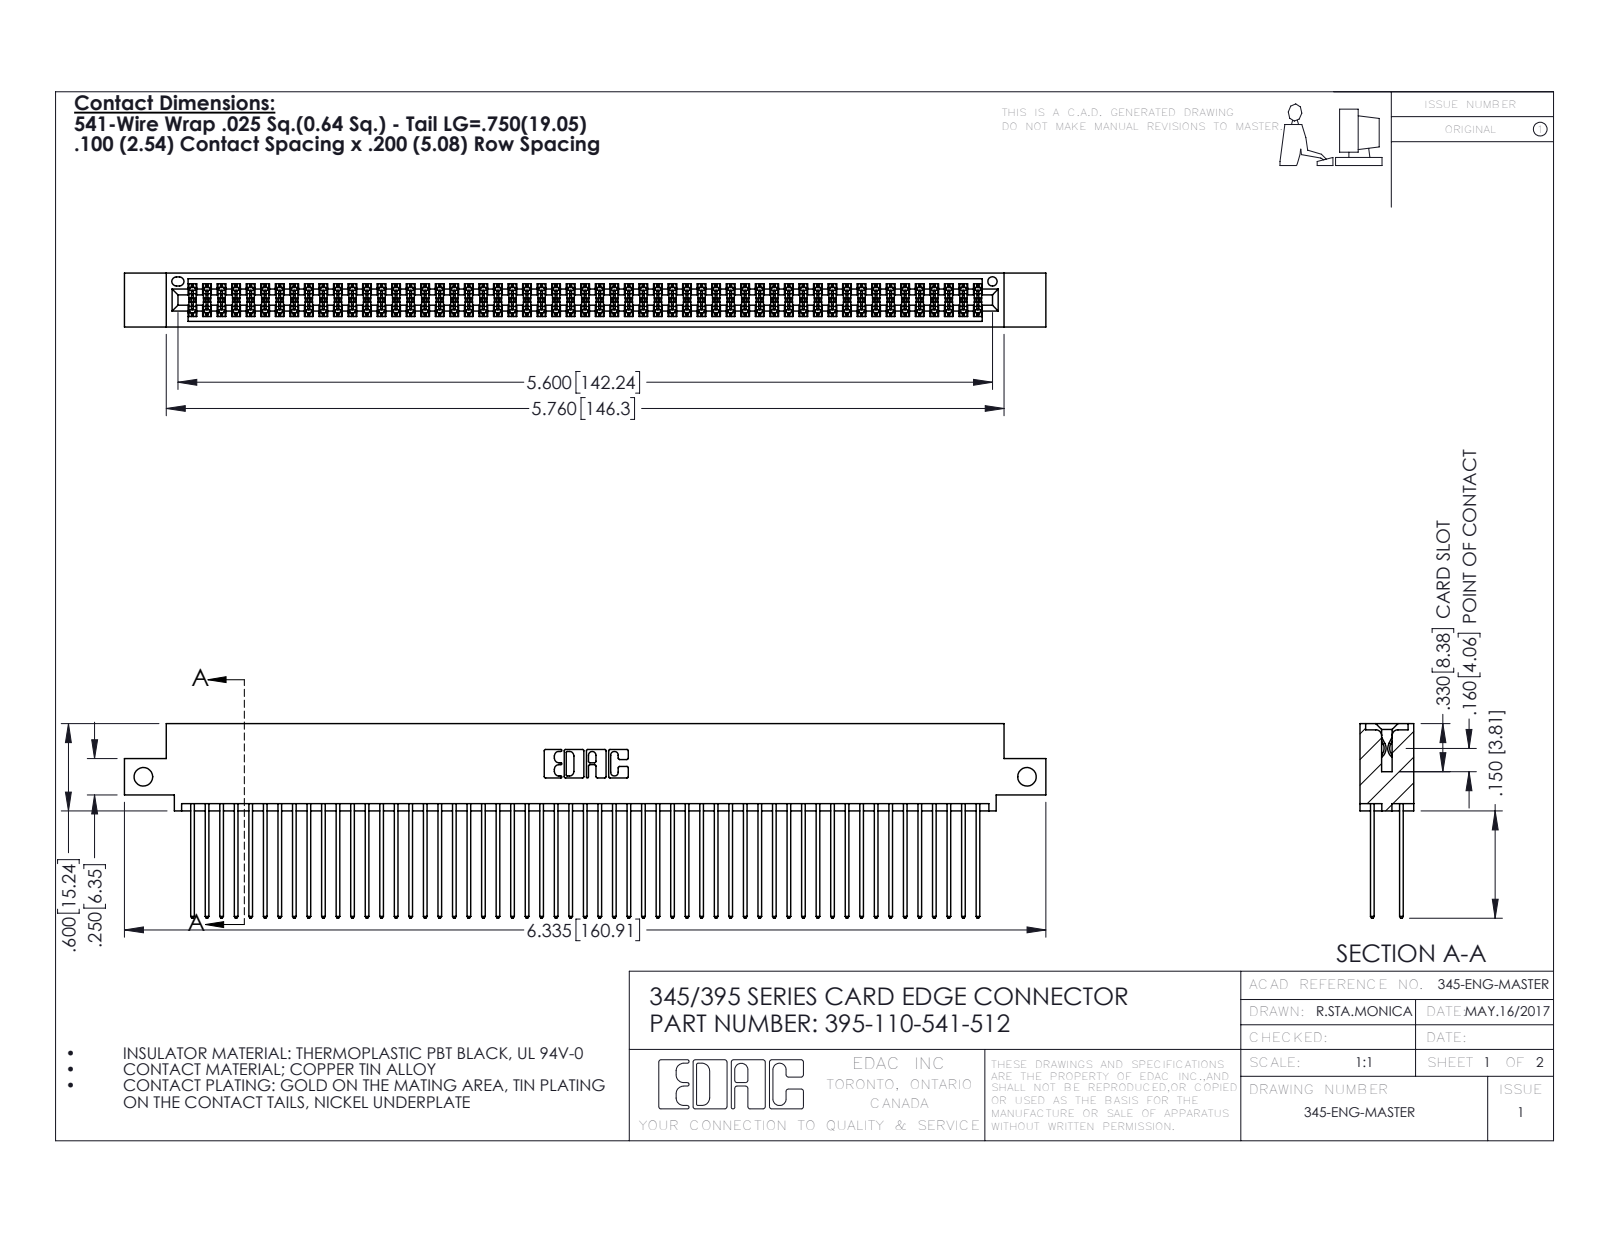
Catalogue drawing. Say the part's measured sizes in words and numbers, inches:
The part is named "345 Part_0.110 Offset - Side Mount; 345-292-001_345-293-141; 395-110-541-512". Its 3-D file was written by "SolidWorks 2016 (CONFIG_CONTROL_DESIGN)". It is 111 solids with 5630 faces: 3714 planar, 1916 cylindrical and 0 other. Overall it measures 6.335 by 1.337 by 0.37 inches. Its volume is 0.99 cubic inches and its surface area 42.09 square inches. Round holes: 2 of diameter 0.128, 1 of diameter 0.064. Partial cylindrical surfaces (rounded edges, fillets, slot ends): 165 of radius 0.006, 110 of radius 0.01, 22 of radius 0.01, 6 of radius 0.007, 6 of radius 0.031, 3 of radius 0.026, 2 of radius 0.014, 2 of radius 0.019. The main face-to-face distances are 0.298, 0.072, 0.2, 0.098, 0.272, 0.025, 0.225, 0.37, 0.175, 0.149. The hole center spacings are 6.075.
